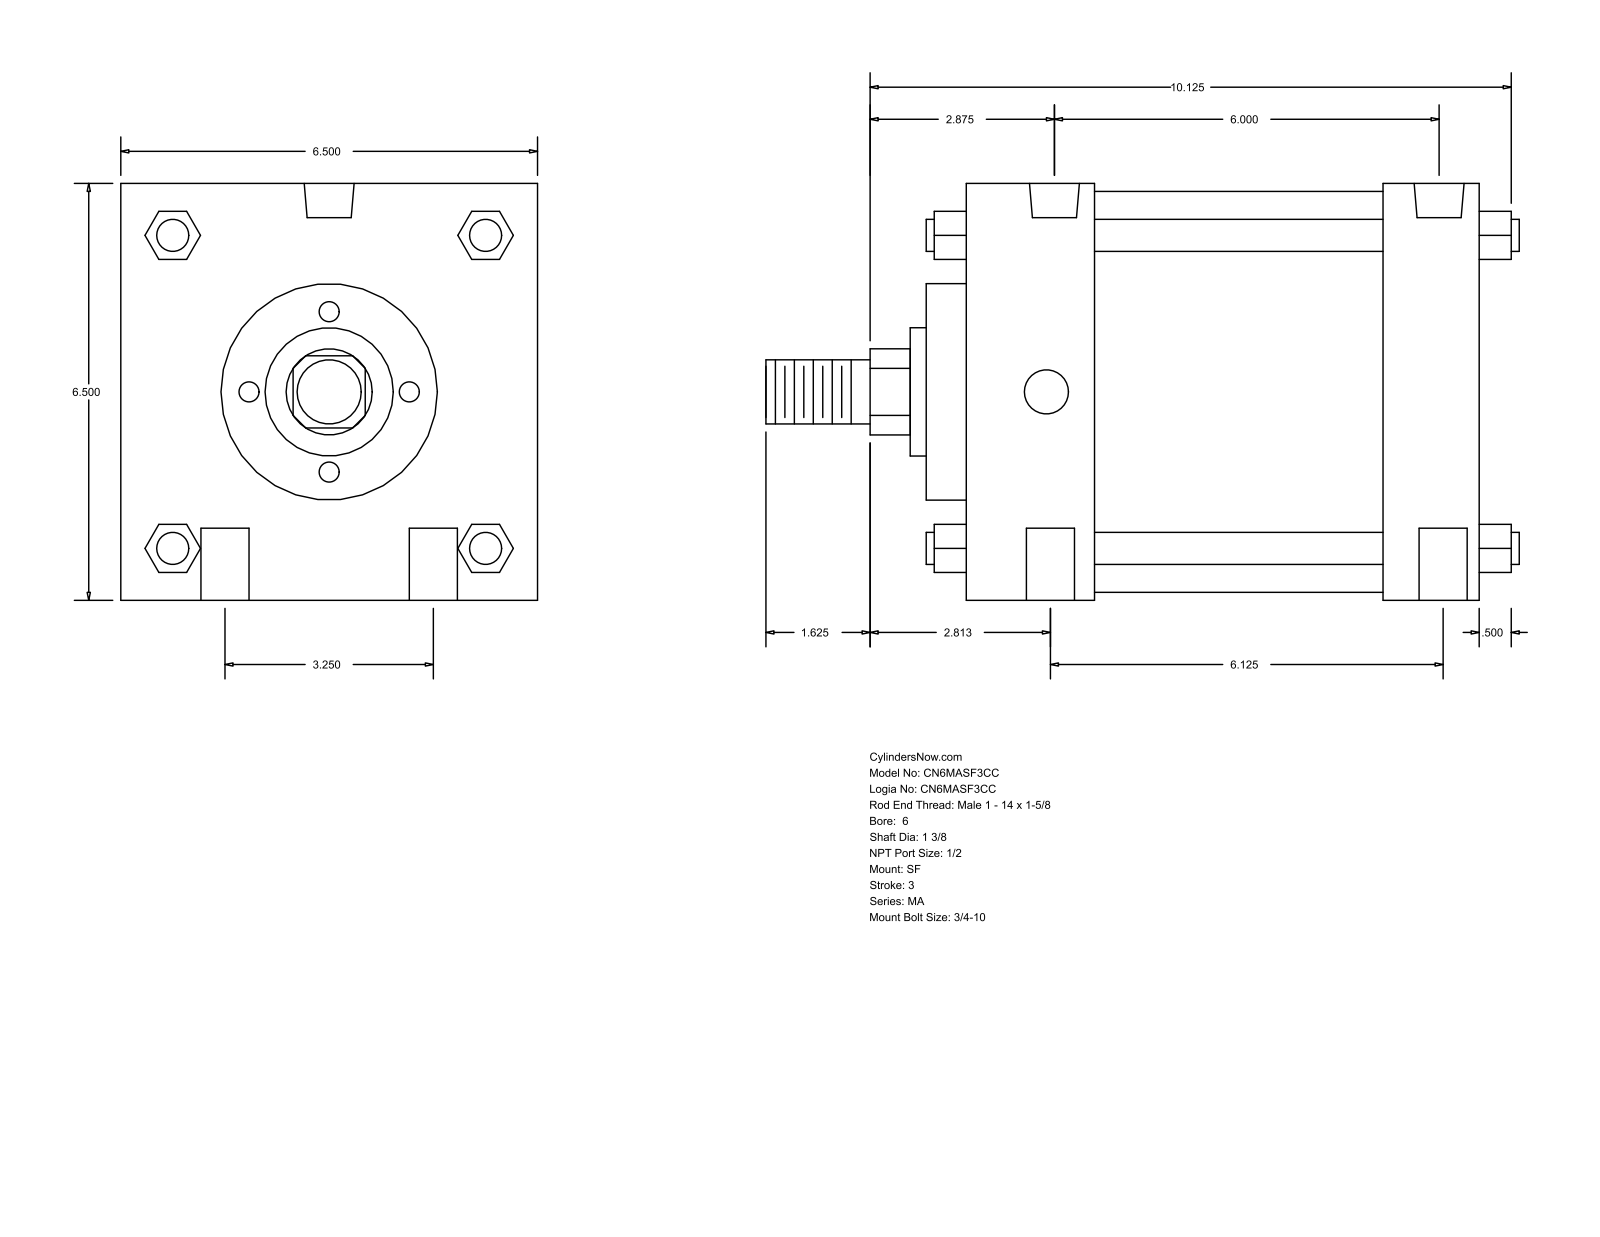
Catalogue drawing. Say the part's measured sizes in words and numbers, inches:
The part is named "MA_SF__0600_1.375". Its 3-D file was written by "GSSL Pune (CONFIG_CONTROL_DESIGN)". It is 0 solids with 126 faces: 95 planar, 31 cylindrical and 0 other. Overall it measures 11.75 by 6.5 by 6.5 inches. Round holes: 4 of diameter 0.75, 2 of diameter 0.687, 2 of diameter 0.778. Round bosses or shafts: 4 of diameter 0.5, 1 of diameter 6.25, 1 of diameter 3.375, 1 of diameter 2, 1 of diameter 1.375, 1 of diameter 1. Partial cylindrical surfaces (rounded edges, fillets, slot ends): 1 of radius 0.672. The main face-to-face distances are 6.5, 8, 6, 2, 1.5, 4.5, 2.625, 0.625, 7.125, 8.625. The hole center spacings are 1.626, 3.25, 6, 6.125, 6.276, 6.276, 6.933.
